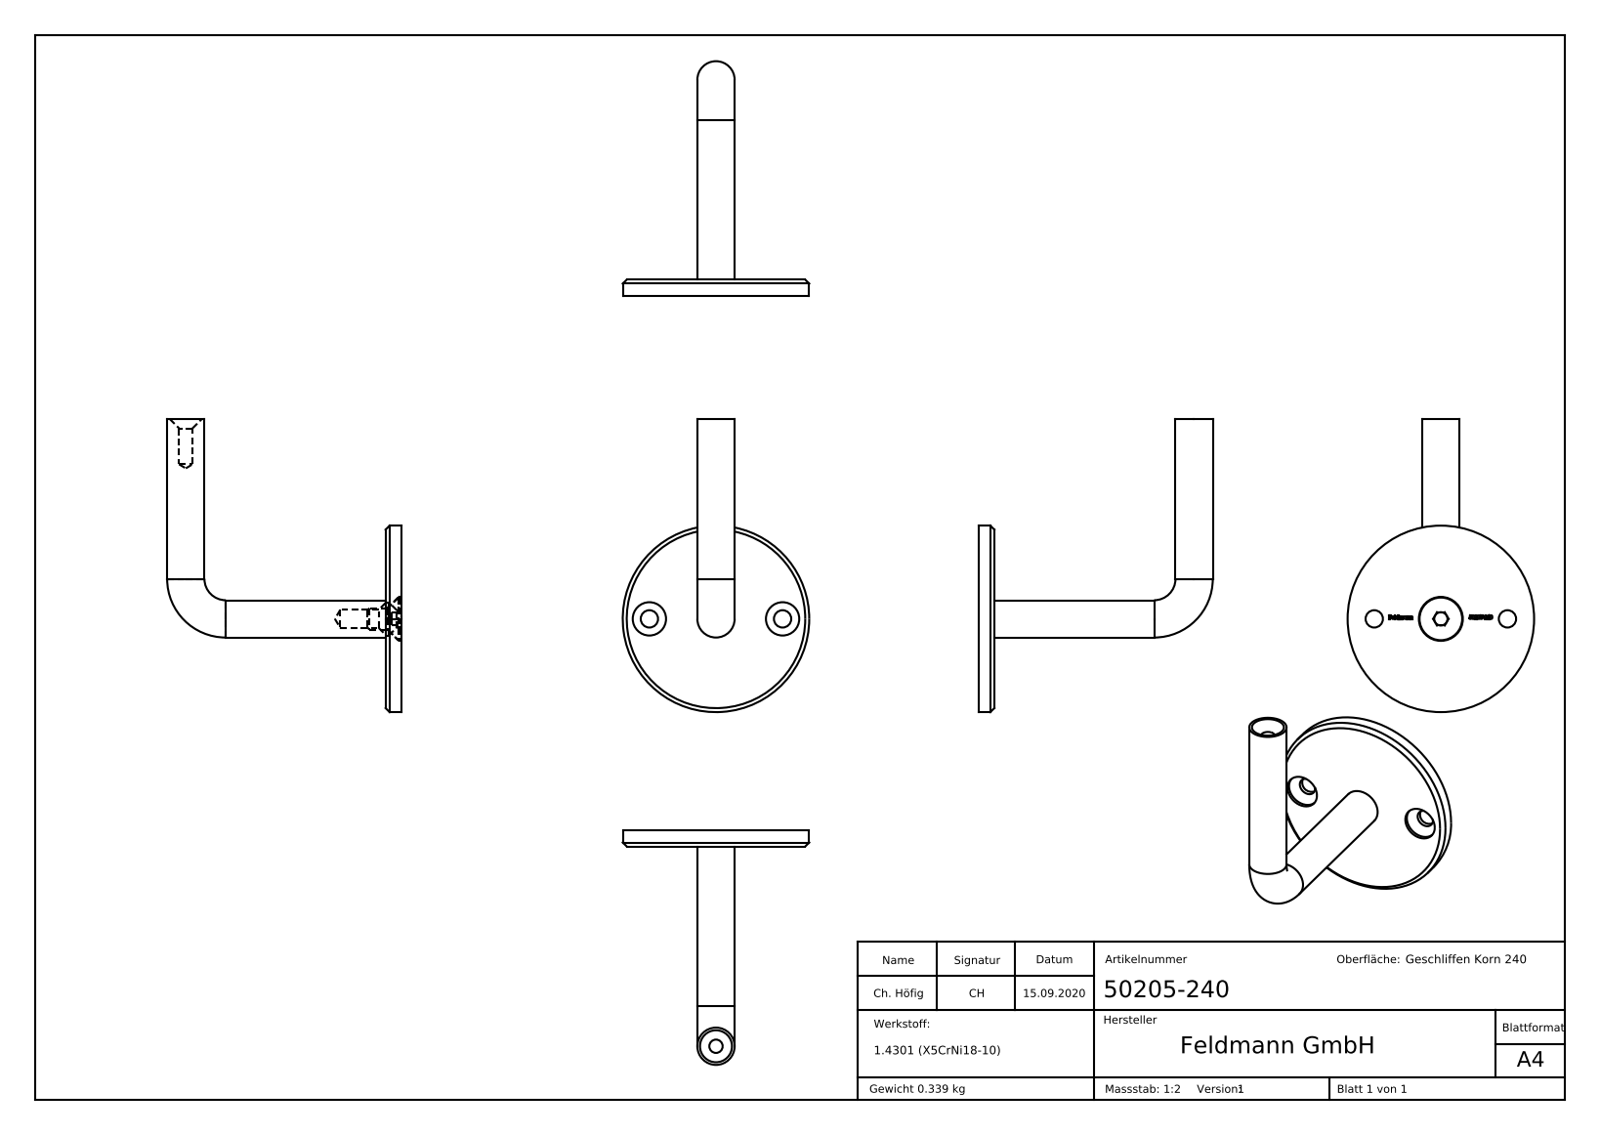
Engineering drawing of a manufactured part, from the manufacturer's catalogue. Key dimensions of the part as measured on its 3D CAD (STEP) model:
Part name (STEP PRODUCT): 50205-240 Teil1; 50205-240; DIN-7991 M3-M10_DIN7991 M8x12; 50205-240 Teil2 (+3 more)
STEP written by: SolidWorks 2018 (CONFIG_CONTROL_DESIGN)
Units: millimetres
Bodies: 3 solids, 290 faces (137 planar, 26 cylindrical, 127 other)
Overall size (bounding box): 110 × 88 × 70
Volume: 42 946 mm³ · Surface area: 16 909 mm²
Round holes (diameter × count): ⌀6.5 ×2, ⌀12.5 ×2, ⌀5 ×1, ⌀6.8 ×1, ⌀8.5 ×1, ⌀16.5 ×1
Round bosses / shafts (diameter × count): ⌀14 ×2, ⌀70 ×1, ⌀16 ×1, ⌀8 ×1
Main face-to-face distances: 6, 0.85, 5.15, 12.85, 12, 6.85, 5, 77.5, 72.5, 0.75
Hole centre spacings: 25, 50
